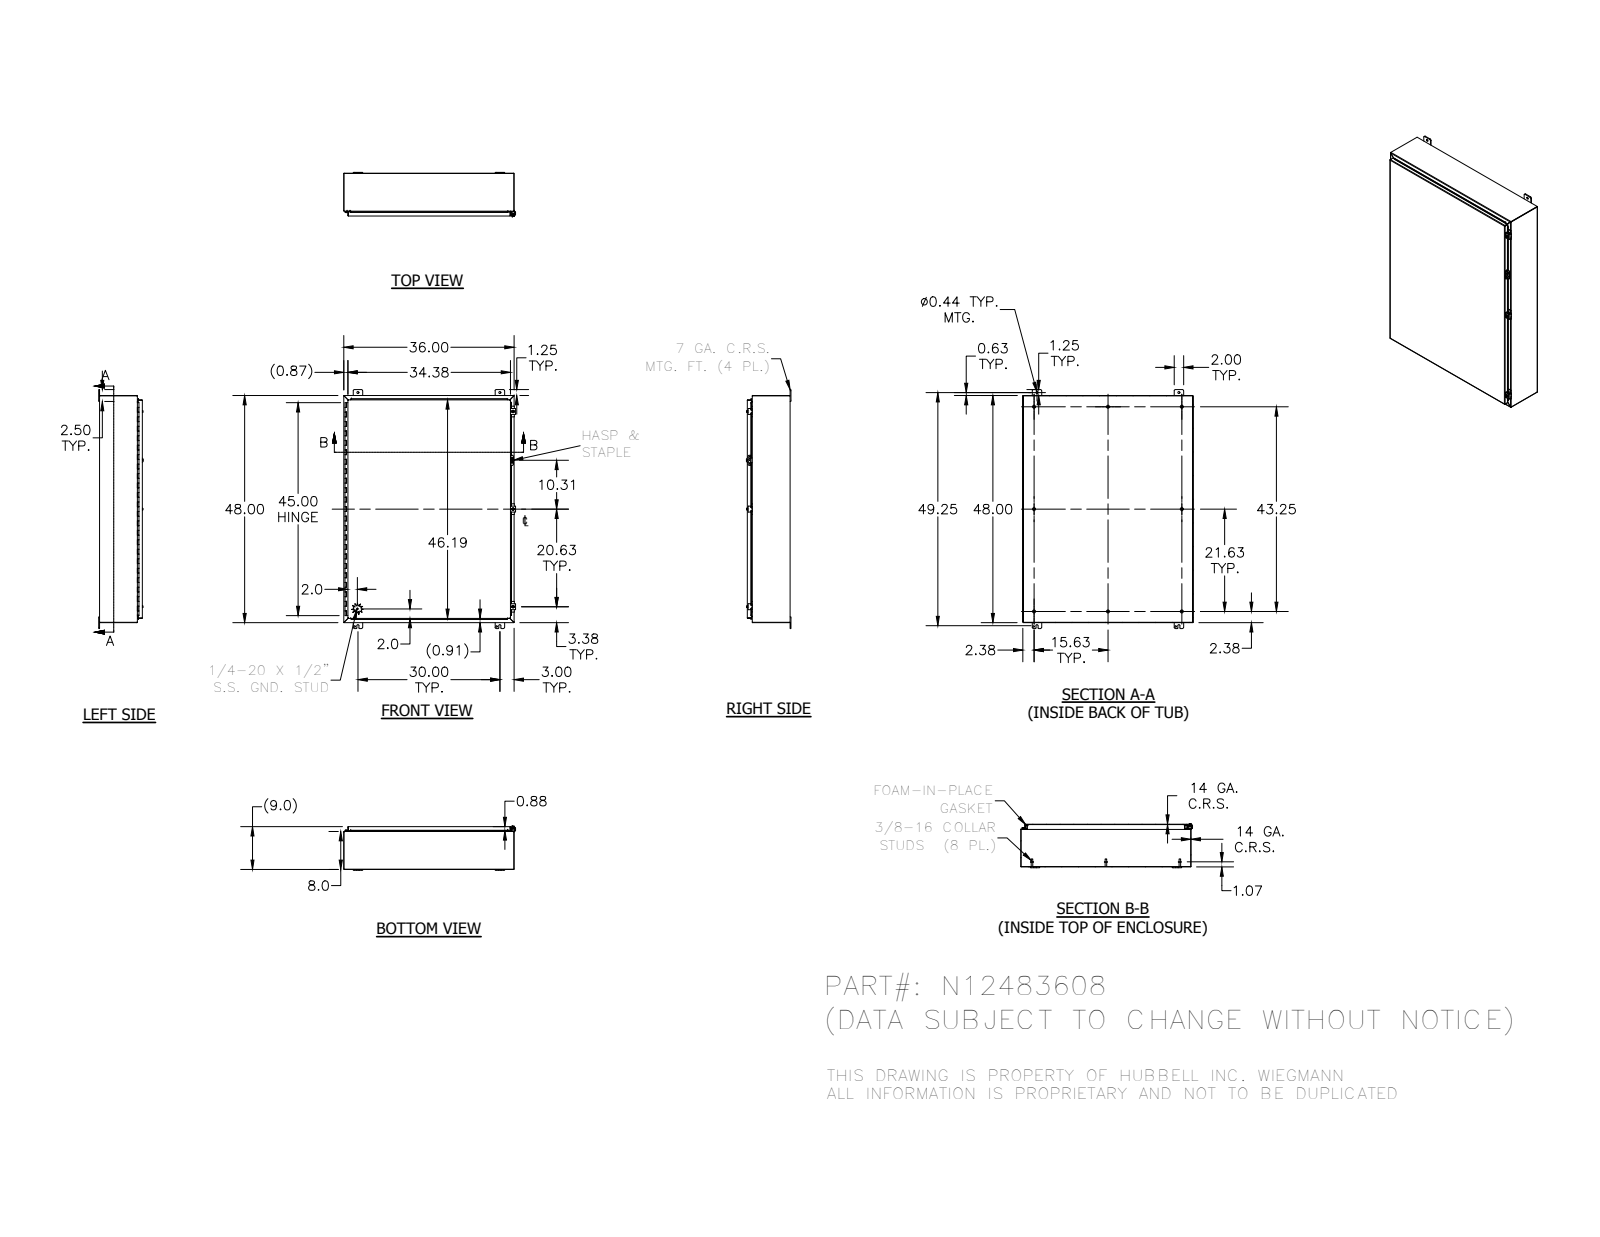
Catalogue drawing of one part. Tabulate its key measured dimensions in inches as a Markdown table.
| quantity | value |
| --- | --- |
| part name | N12483608; 34840; 38413; N123608TB (+8 more) |
| STEP written by | Autodesk Inventor 2012 (AUTOMOTIVE_DESIGN) |
| units | inches |
| bodies | 38 solids, 1249 faces (734 planar, 392 cylindrical, 123 other) |
| overall size | 50.5 × 36.311 × 9.41 |
| volume | 410.3 in³ |
| surface area | 10 849 in² |
| round holes (diameter × count) | 0.313 × 4, 0.438 × 4, 0.11 × 3, 0.211 × 3, 0.281 × 3, 0.3 × 3, 0.125 × 1, 0.156 × 1, 0.5 × 1 |
| round bosses / shafts (diameter × count) | 0.625 × 8, 0.33 × 8, 0.25 × 5, 0.52 × 3, 0.5 × 3, 0.35 × 3, 0.337 × 1, 0.12 × 1 |
| partial cylindrical surfaces (radius × count) | 0.03 × 39, 0.125 × 27, 0.25 × 27, 0.031 × 21, 0.105 × 21, 0.063 × 15, 0.1 × 6, 0.141 × 6 |
| main face-to-face distances | 0.074, 8.959, 8.885, 9.033, 35.926, 47.926, 7.926, 1.033, 35.852, 36 |
| hole center spacings | 1.593, 30, 48, 56.604, 0.791, 10.327, 29.348, 30.72 |
